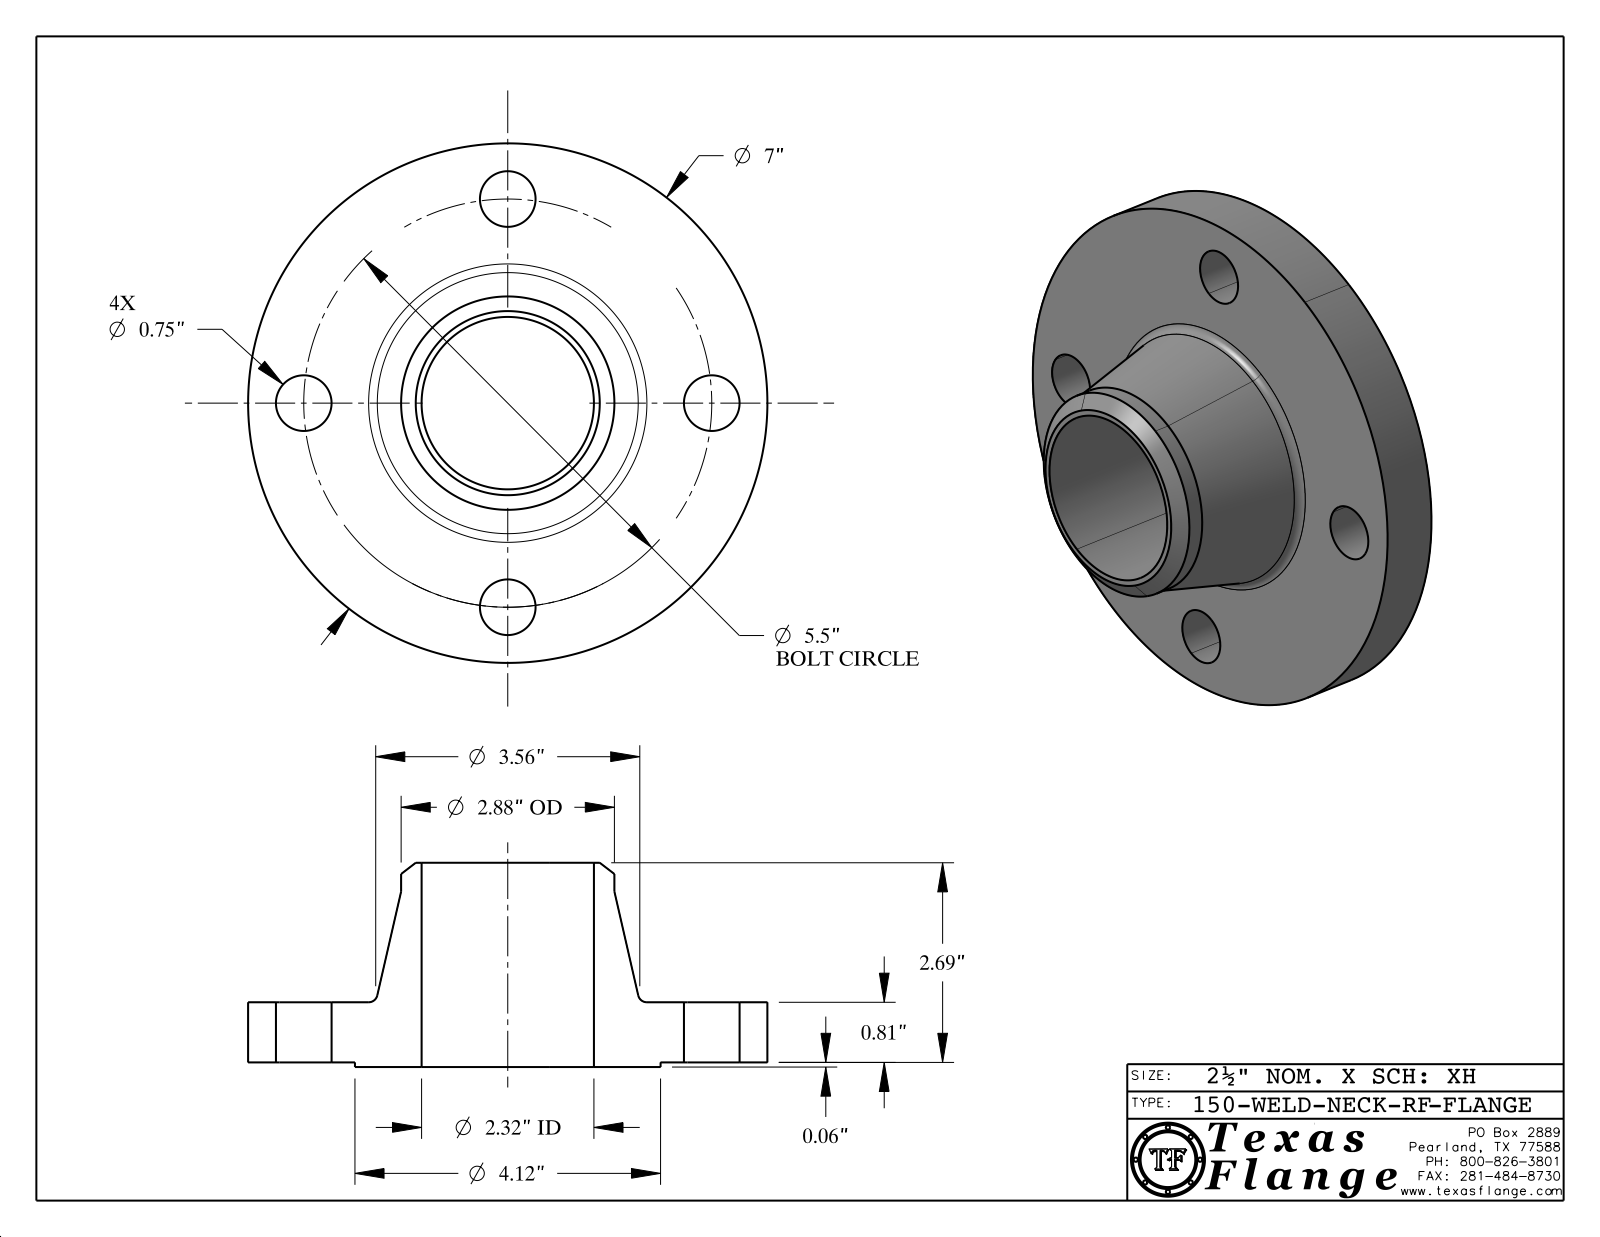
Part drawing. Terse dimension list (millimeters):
name: 150-WELD-NECK-RF
written by: CATIA V5 STEP AP214 (AUTOMOTIVE_DESIGN)
unit: mm
bodies: 1 solid, 411 faces (369 planar, 36 cylindrical, 6 other)
size: 177.8 × 177.8 × 69.9
volume: 549 000 mm³; area: 81 030 mm²
holes: 4× ⌀19.1, 1× ⌀12.6, 1× ⌀59
bosses: 8× ⌀0.8, 1× ⌀177.8, 1× ⌀104.6, 1× ⌀73, 1× ⌀9.9
face distances: 20.6, 1.6, 22.1, 69.9, 68.3, 47.8, 21.8, 20.2, 0.4, 48.1
hole spacings: 69.9, 98.8, 53.5, 129.1, 139.7
